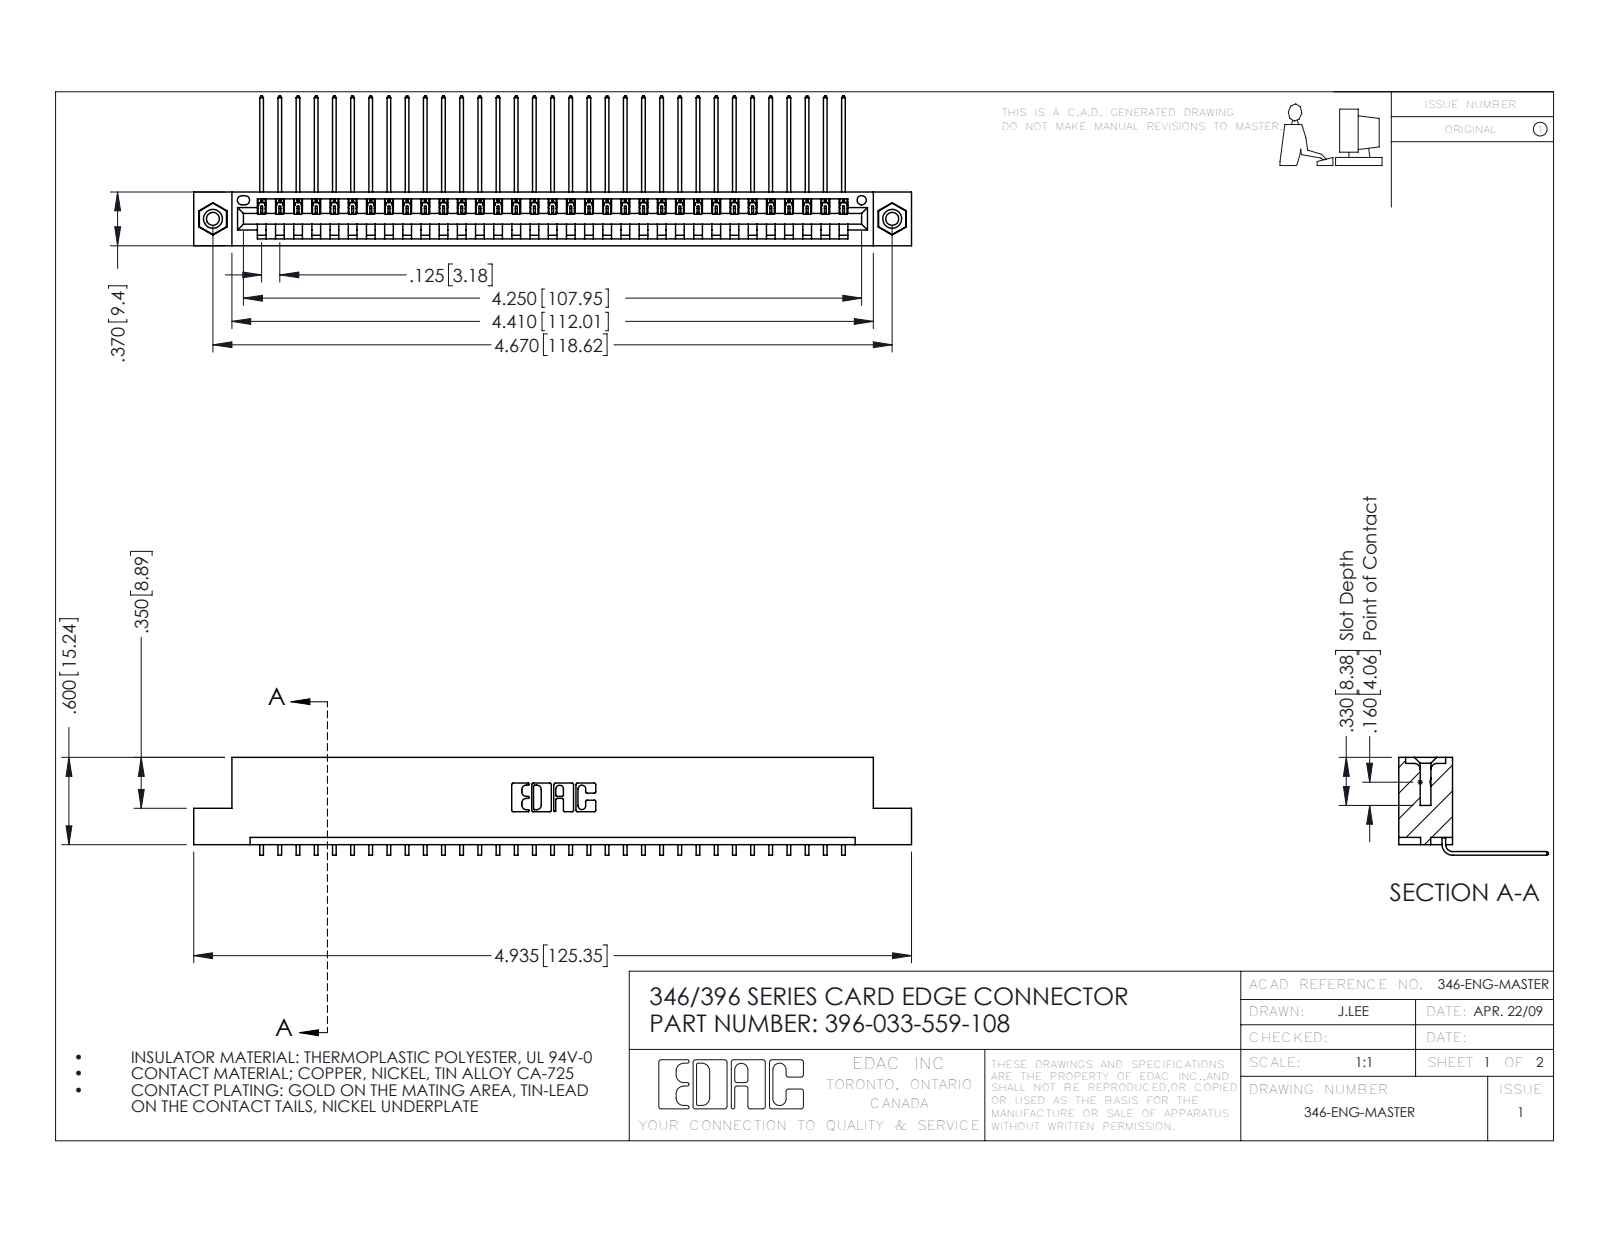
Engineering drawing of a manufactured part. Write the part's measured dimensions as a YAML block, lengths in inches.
part_name: "396-033-559-108; 345-292-001_558 559 Tail - 1; 345-250-001_345-250-003-102; 346 Part_Flush Mounting Lugs - 0.156 Dia-TI"
step_written_by: "SolidWorks 2016 (CONFIG_CONTROL_DESIGN)"
units: inches
bodies: {solids: 36, faces: 2162, planar: 1494, cylindrical: 652, other: 16}
overall_size: [4.935, 1.03, 0.673]
volume: 0.735
surface_area: 24.23
round_holes:
  - {diameter: 0.089, count: 2}
  - {diameter: 0.125, count: 2}
  - {diameter: 0.156, count: 2}
  - {diameter: 0.064, count: 1}
round_bosses_or_shafts:
  - {diameter: 0.155, count: 2}
partial_cylinders:
  - {radius: 0.006, count: 66}
  - {radius: 0.01, count: 22}
  - {radius: 0.007, count: 6}
  - {radius: 0.031, count: 6}
  - {radius: 0.026, count: 3}
  - {radius: 0.031, count: 2}
  - {radius: 0.04, count: 2}
  - {radius: 0.014, count: 1}
face_to_face_distances: [0.048, 0.322, 0.37, 0.25, 0.072, 0.025, 0.298, 0.148, 0.222, 0.1]
hole_center_spacings: [0.246, 4.462, 4.67]
